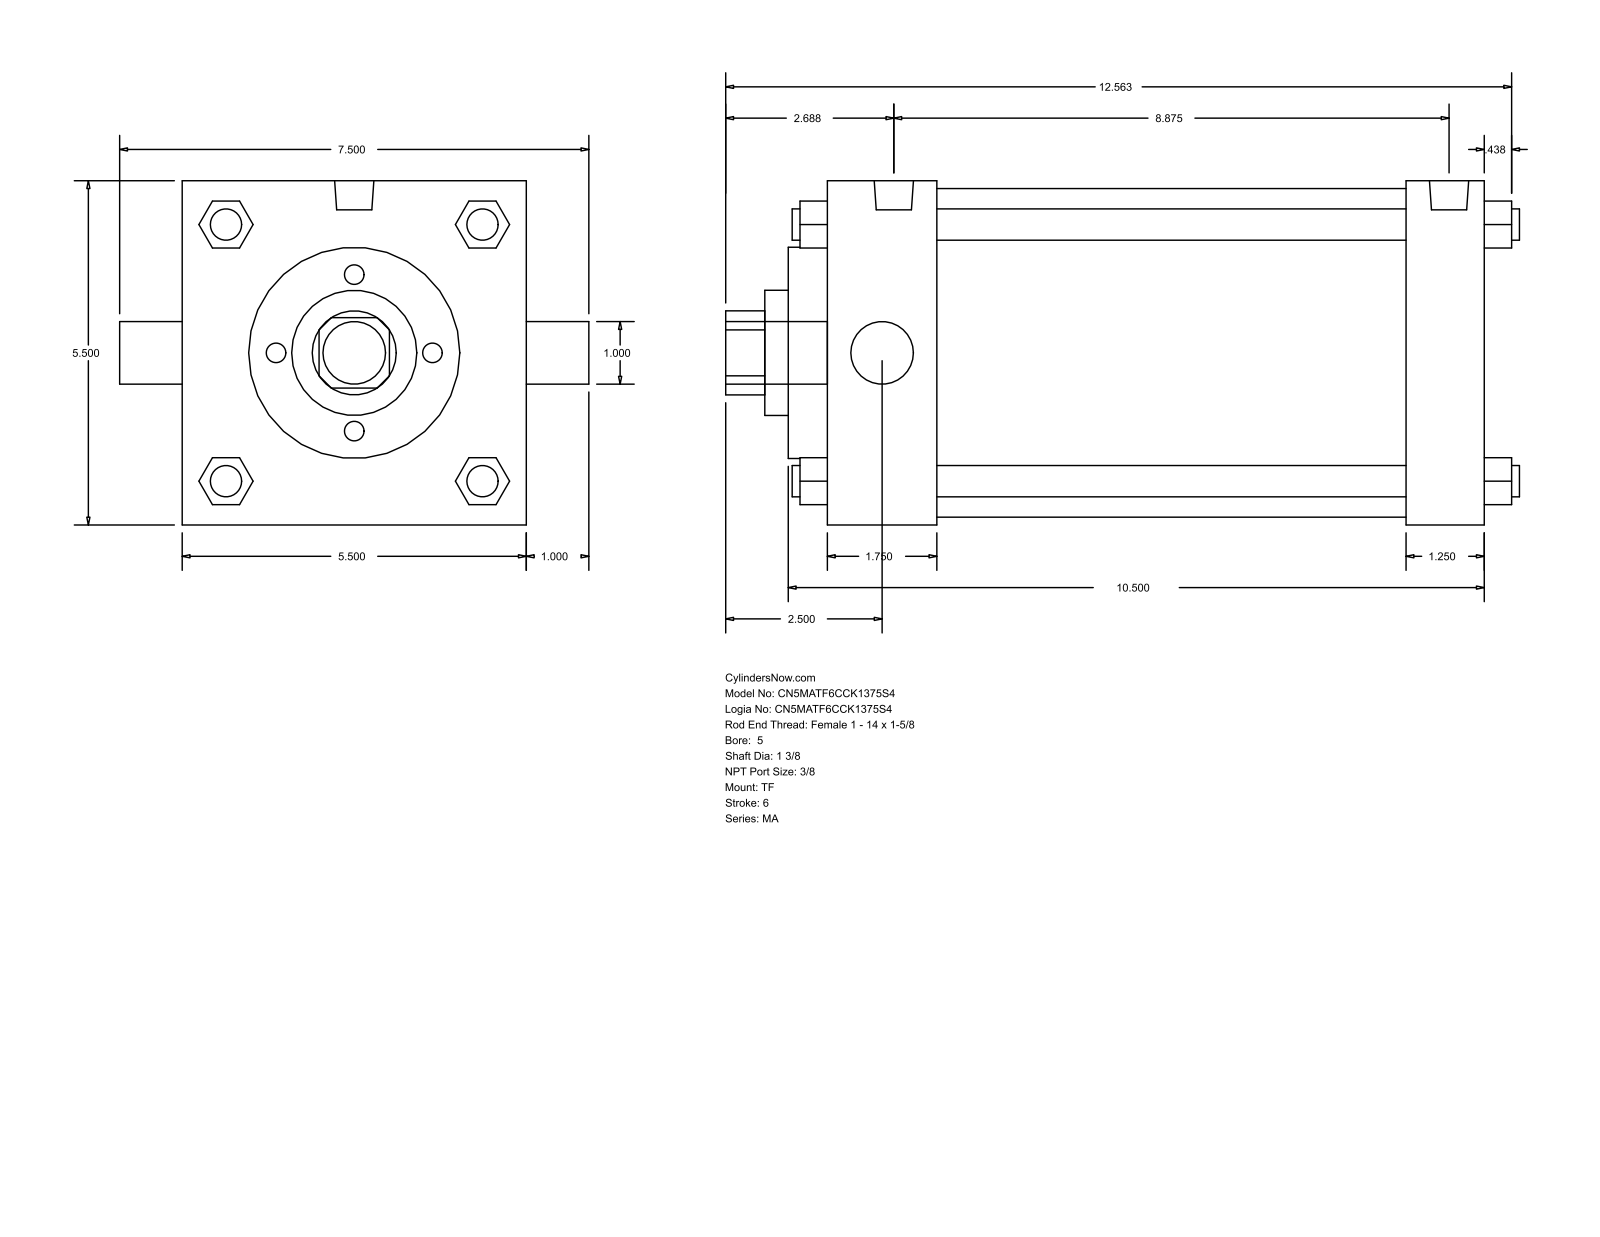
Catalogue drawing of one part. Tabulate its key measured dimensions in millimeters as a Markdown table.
| quantity | value |
| --- | --- |
| part name | MA_TF__0500_1.375 |
| STEP written by | GSSL Pune (CONFIG_CONTROL_DESIGN) |
| units | millimeters |
| bodies | 0 solids, 122 faces (93 planar, 29 cylindrical, 0 other) |
| overall size | 322.26 × 190.5 × 139.7 |
| round holes (diameter × count) | 25.4 × 1, 34.92 × 1, 50.8 × 1, 85.72 × 1, 133.35 × 1 |
| round bosses / shafts (diameter × count) | 12.7 × 4, 11.11 × 3, 15.93 × 2, 25.4 × 1 |
| partial cylindrical surfaces (radius × count) | 17.06 × 1 |
| main face-to-face distances | 139.7, 266.71, 234.96, 31.75, 44.45, 190.51, 222.26, 15.87, 60.32, 250.83 |
